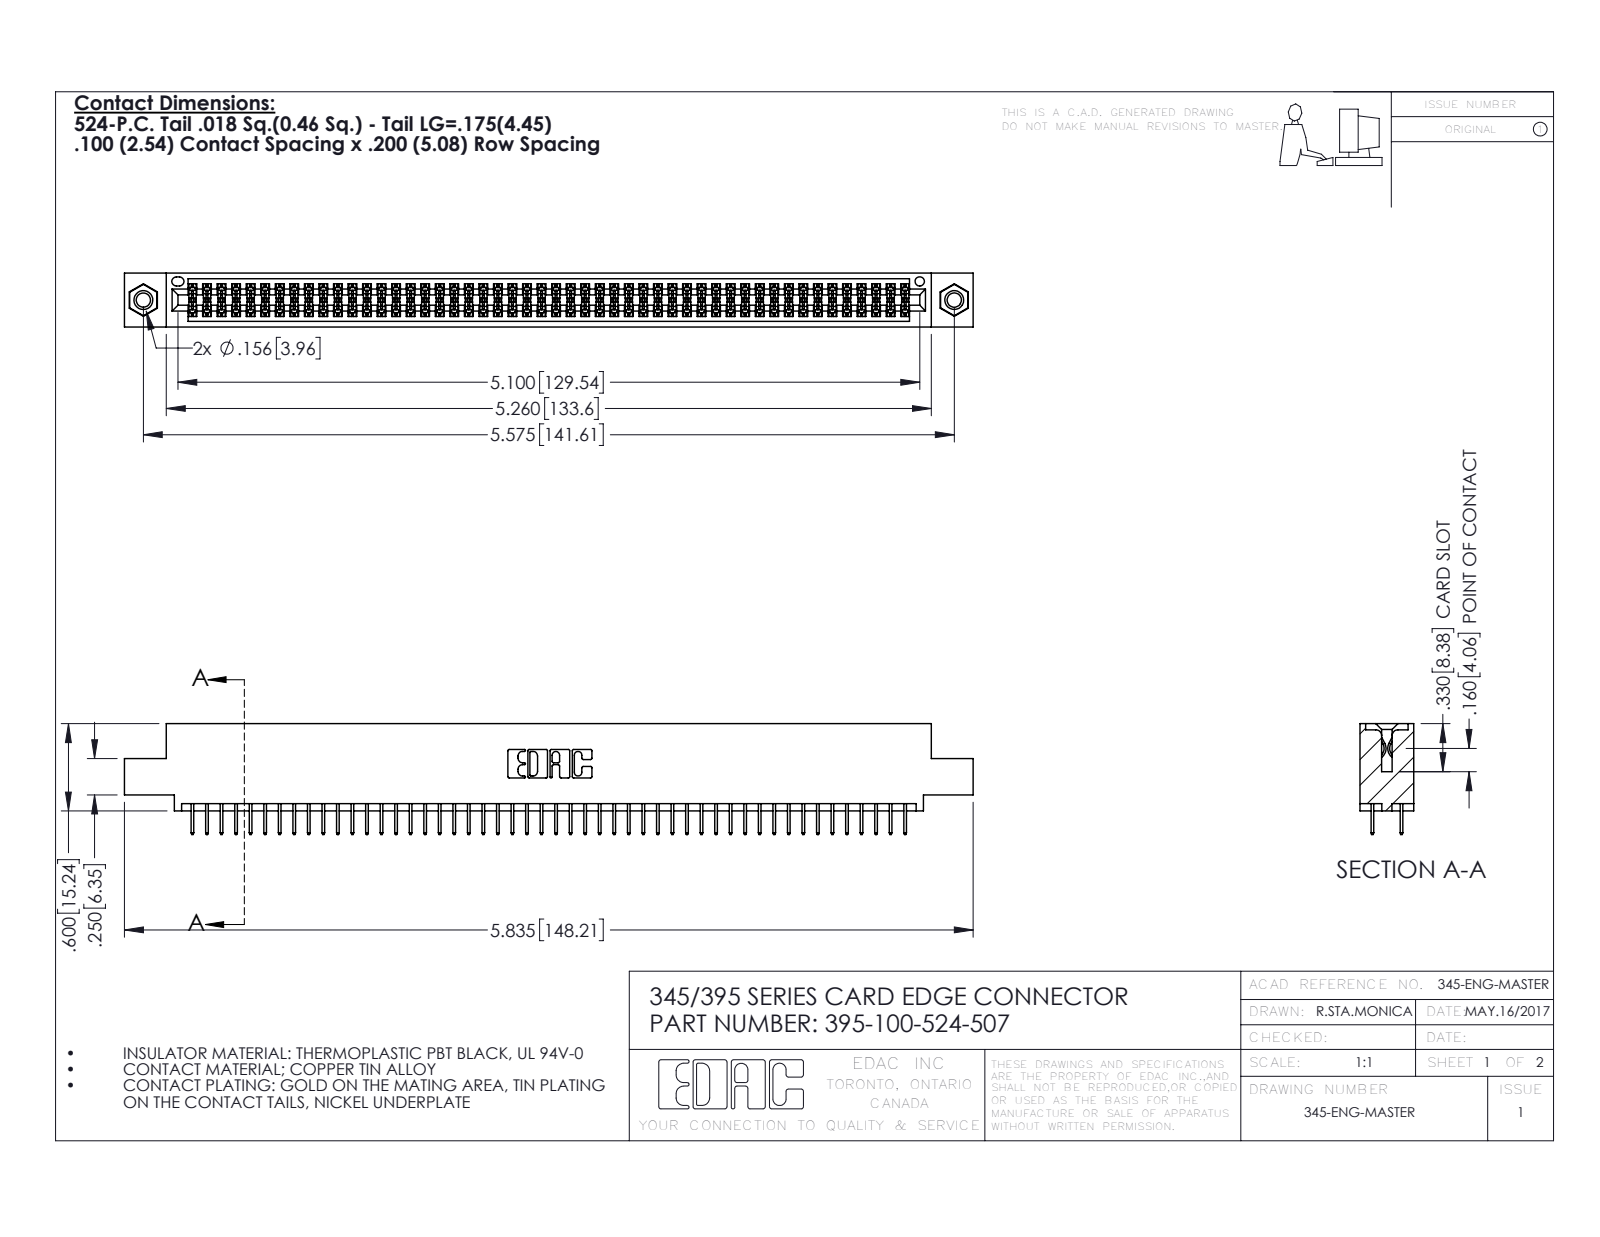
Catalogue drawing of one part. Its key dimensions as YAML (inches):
part_name: "395-100-524-507; 345-250-001_345-250-005-103; 345-292-001_345-293-124; 345 Part_0.110 Offset - 0.156 Dia-TI"
step_written_by: "SolidWorks 2016 (CONFIG_CONTROL_DESIGN)"
units: inches
bodies: {solids: 103, faces: 5590, planar: 4016, cylindrical: 1558, other: 16}
overall_size: [5.835, 0.762, 0.37]
volume: 0.869
surface_area: 32.42
round_holes:
  - {diameter: 0.098, count: 2}
  - {diameter: 0.125, count: 2}
  - {diameter: 0.156, count: 2}
  - {diameter: 0.064, count: 1}
round_bosses_or_shafts:
  - {diameter: 0.155, count: 2}
partial_cylinders:
  - {radius: 0.006, count: 150}
  - {radius: 0.01, count: 22}
  - {radius: 0.007, count: 6}
  - {radius: 0.031, count: 6}
  - {radius: 0.026, count: 3}
  - {radius: 0.014, count: 2}
  - {radius: 0.019, count: 2}
  - {radius: 0.022, count: 2}
face_to_face_distances: [0.072, 0.298, 0.2, 0.37, 0.098, 0.272, 0.025, 0.225, 0.072, 0.175]
hole_center_spacings: [0.27, 5.339, 5.575]
